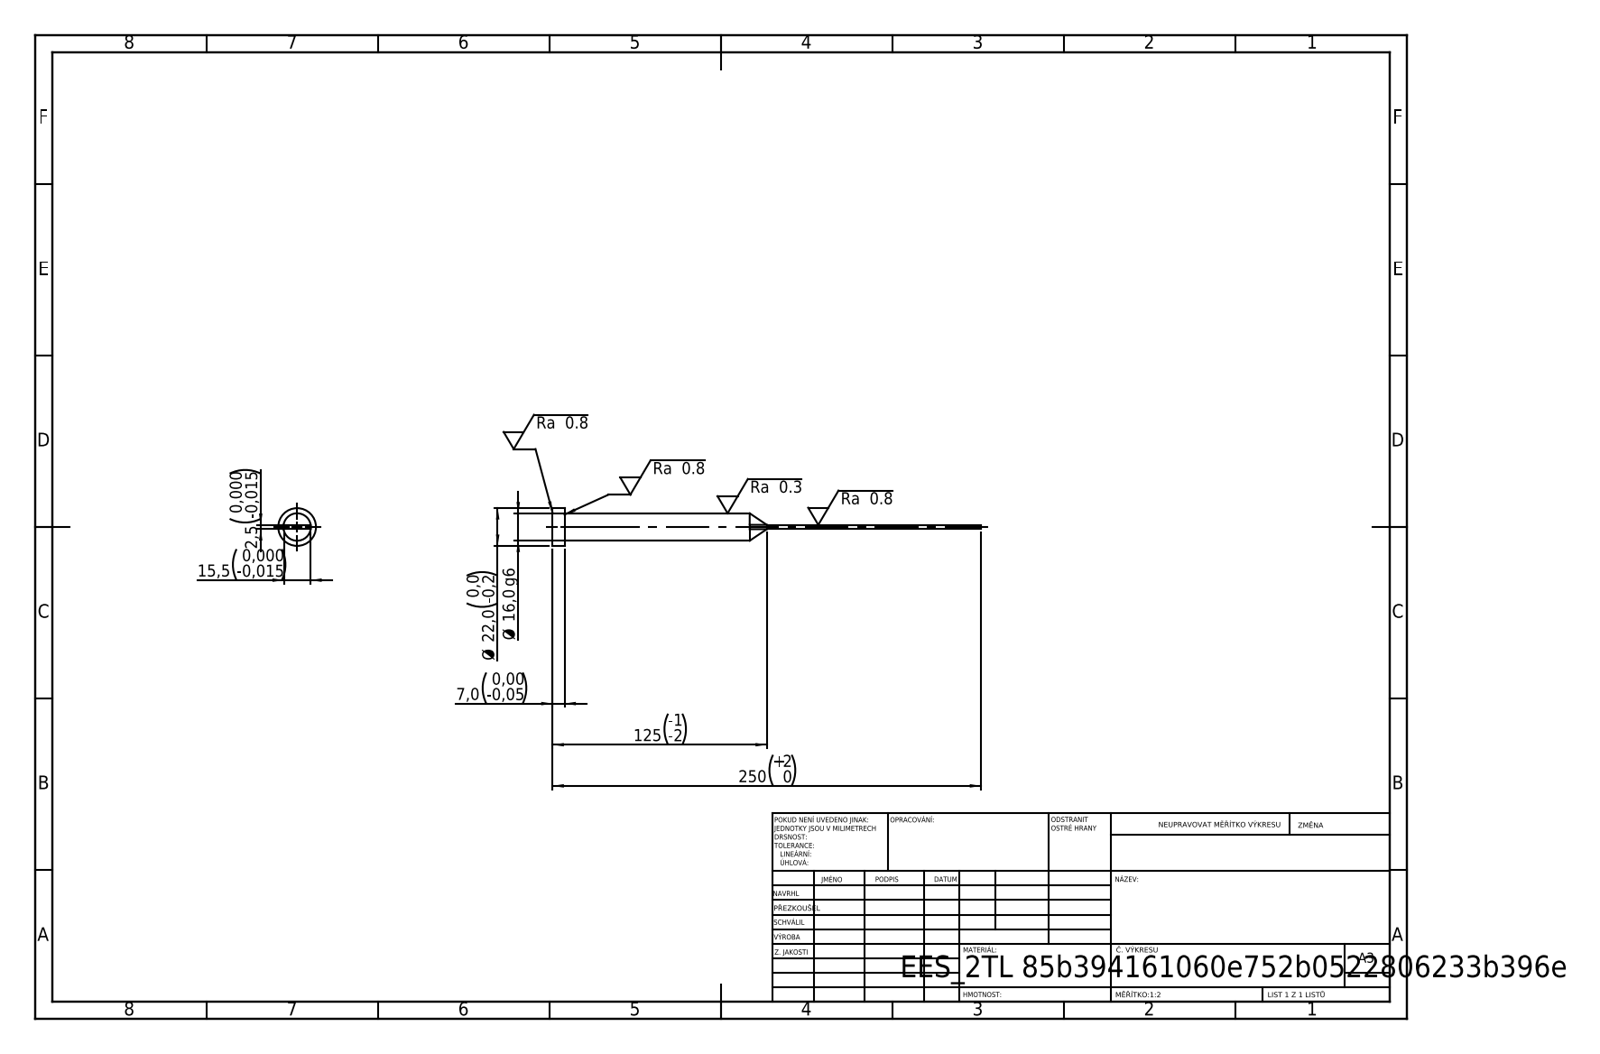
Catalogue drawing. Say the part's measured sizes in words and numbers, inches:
Its 3-D file was written by "SolidWorks 2019 (CONFIG_CONTROL_DESIGN)". It is 1 solid with 15 faces: 7 planar, 4 cylindrical and 4 other. Overall it measures 9.843 by 0.866 by 0.866 inches. Its volume is 1.852 cubic inches and its surface area 17.76 square inches. Round bosses or shafts: 1 of diameter 0.866, 1 of diameter 0.63. The main face-to-face distances are 0.098, 0.61, 0.276, 9.843, 9.567.
